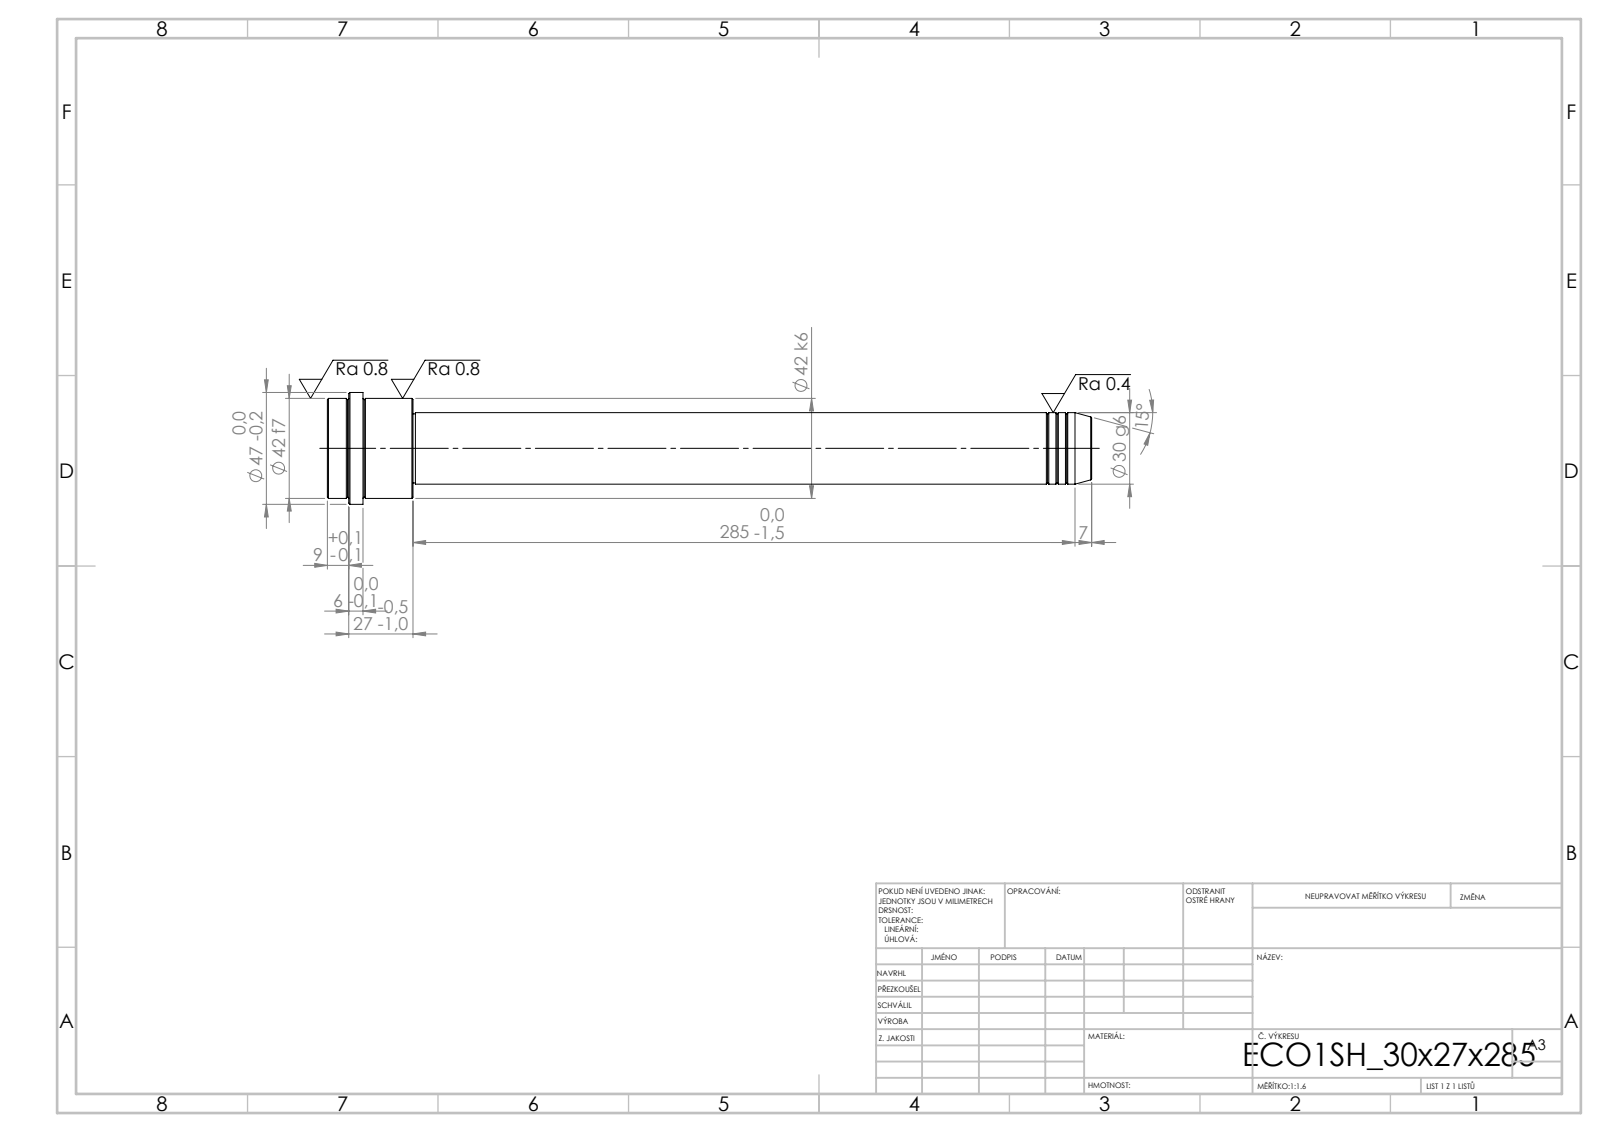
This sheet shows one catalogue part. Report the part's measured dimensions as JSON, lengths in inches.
{"step_written_by": "SolidWorks 2019 (CONFIG_CONTROL_DESIGN)", "units": "inches", "bodies": {"solids": 1, "faces": 52, "planar": 6, "cylindrical": 16, "other": 30}, "overall_size": [12.638, 1.85, 1.85], "volume_in3": 15.41, "surface_area_in2": 54.63, "round_bosses_or_shafts": [[1.85, 1], [1.654, 1], [1.181, 1], [1.142, 1]], "face_to_face_distances": [1.417, 11.22, 12.638, 12.047, 0.827, 0.591, 12.283, 1.063, 0.236, 0.354]}
